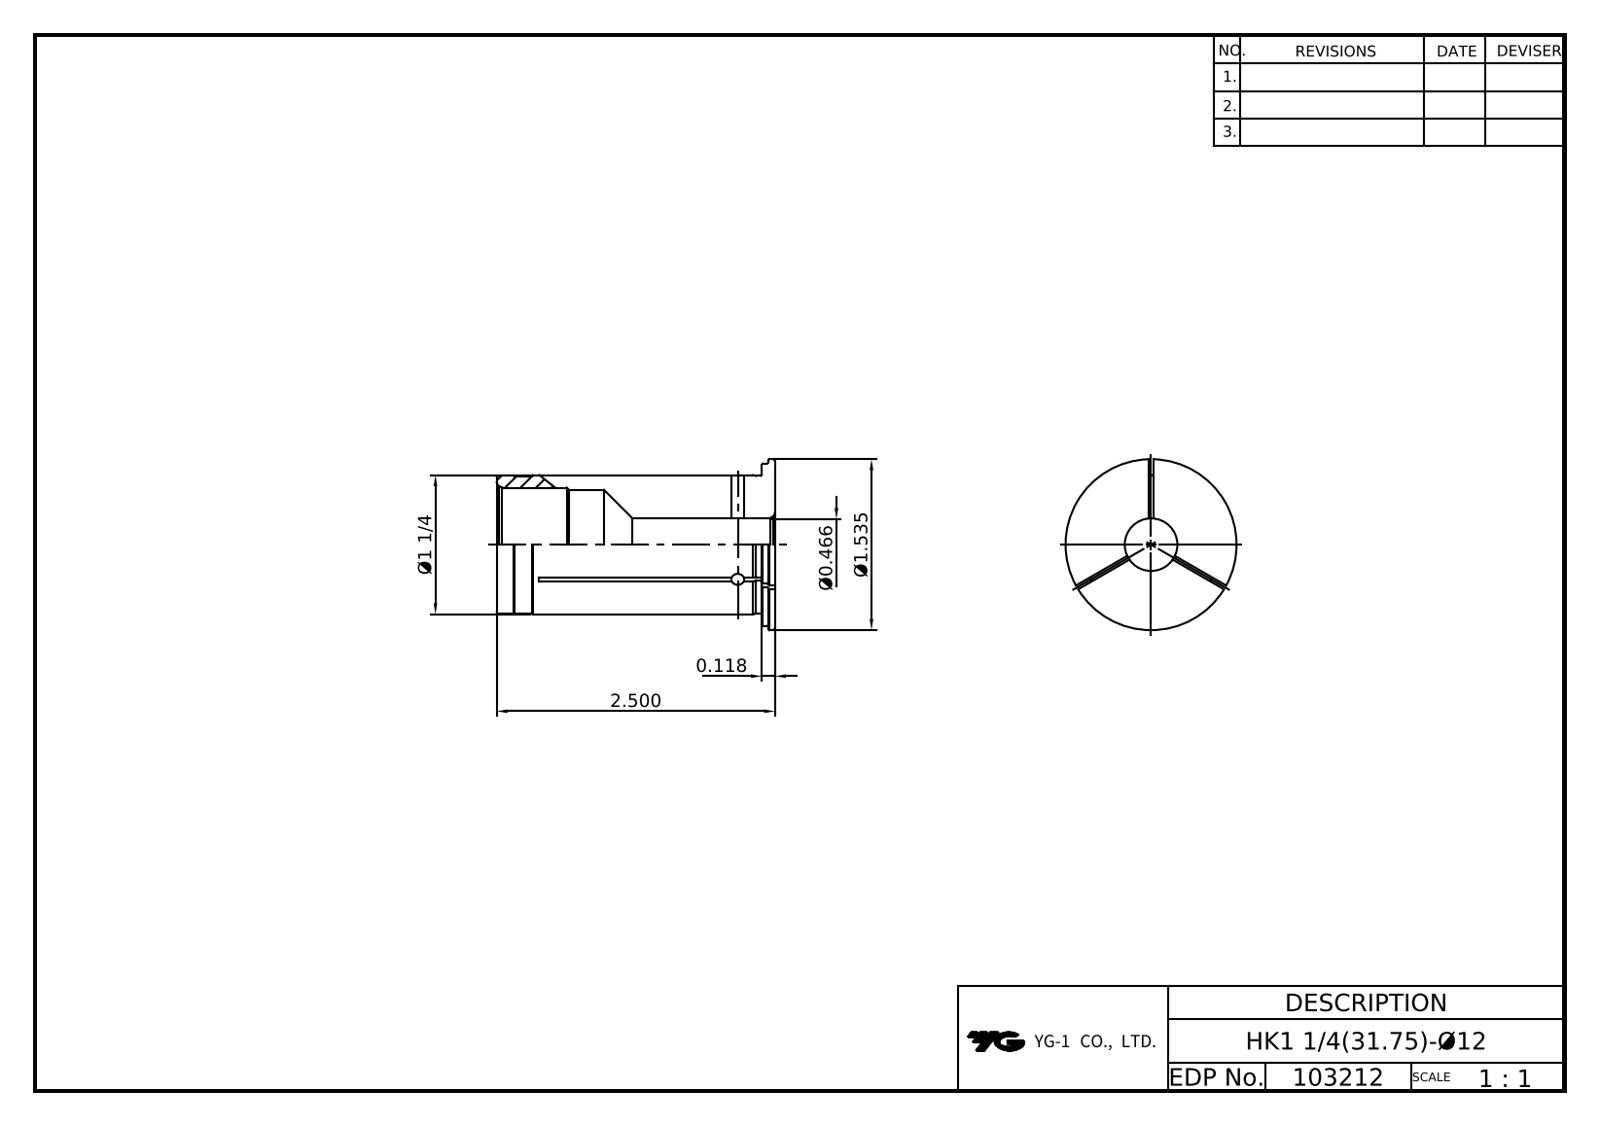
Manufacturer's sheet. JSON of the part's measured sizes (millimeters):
{"part_name": "LO-HK31.75-12", "step_written_by": "Autodesk Inventor 2025 (AP242_MANAGED_MODEL_BASED_3D_ENGINEERING_MIM_LF)", "units": "millimeters", "bodies": {"solids": 1, "faces": 16, "planar": 4, "cylindrical": 6, "other": 6}, "overall_size": [63.5, 39, 39], "volume_mm3": 33127, "surface_area_mm2": 11820, "round_holes": [[12, 1], [25, 1], [26, 1]], "round_bosses_or_shafts": [[39, 1], [37, 1], [31.75, 1]], "face_to_face_distances": [63.5, 60.5, 3, 1.5, 62]}
